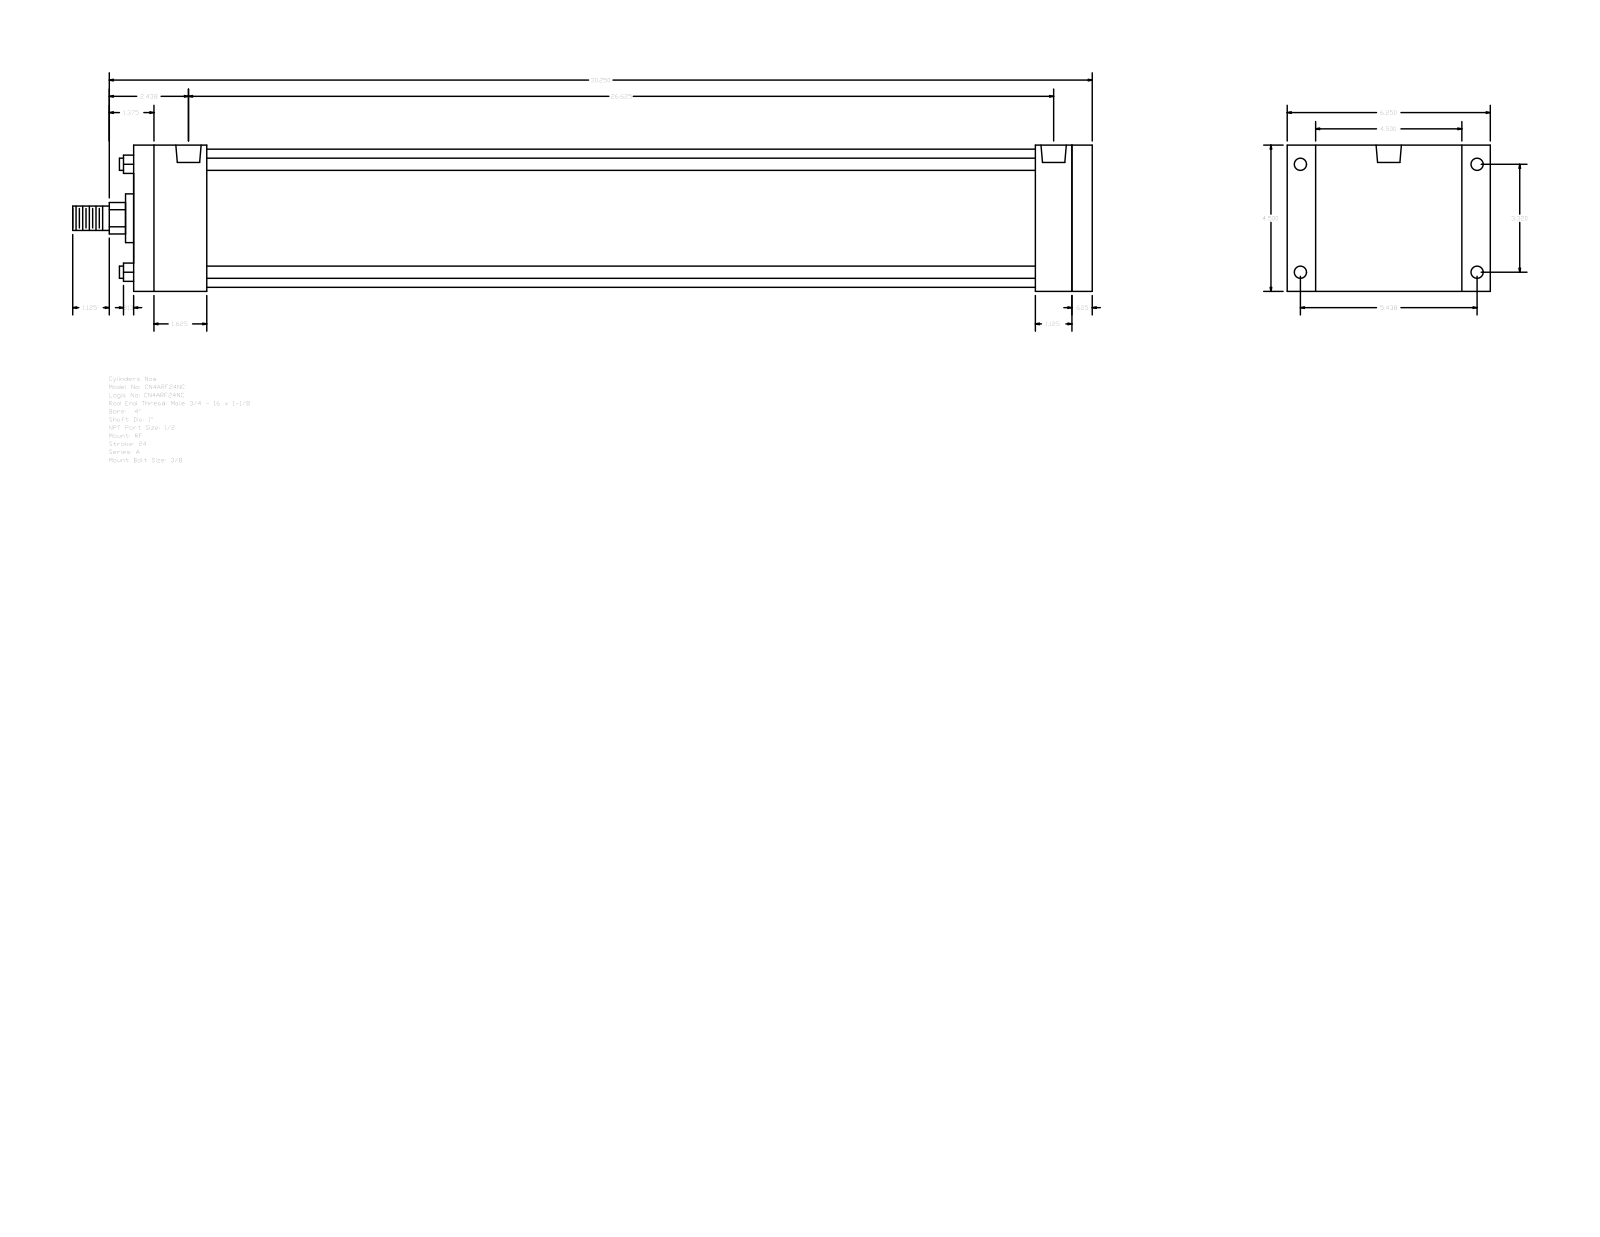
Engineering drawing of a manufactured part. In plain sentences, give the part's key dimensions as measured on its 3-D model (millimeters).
The part is named "A_RF__0400_1". Its 3-D file was written by "GSSL Pune (CONFIG_CONTROL_DESIGN)". It is 0 solids with 92 faces: 64 planar, 28 cylindrical and 0 other. Overall it measures 796.92 by 158.75 by 114.3 millimeters. Round holes: 4 of diameter 8.73, 4 of diameter 9.53, 2 of diameter 19.77. Round bosses or shafts: 4 of diameter 9.53, 1 of diameter 107.95, 1 of diameter 38.1, 1 of diameter 25.4, 1 of diameter 19.05. Partial cylindrical surfaces (rounded edges, fillets, slot ends): 1 of radius 12.29. The main face-to-face distances are 114.3, 749.3, 733.43, 15.87, 22.23, 136.53, 704.85, 28.58, 44.45, 57.15. The hole center spacings are 3.18, 84.32, 138.12, 161.82, 669.92, 673.1, 676.28.
